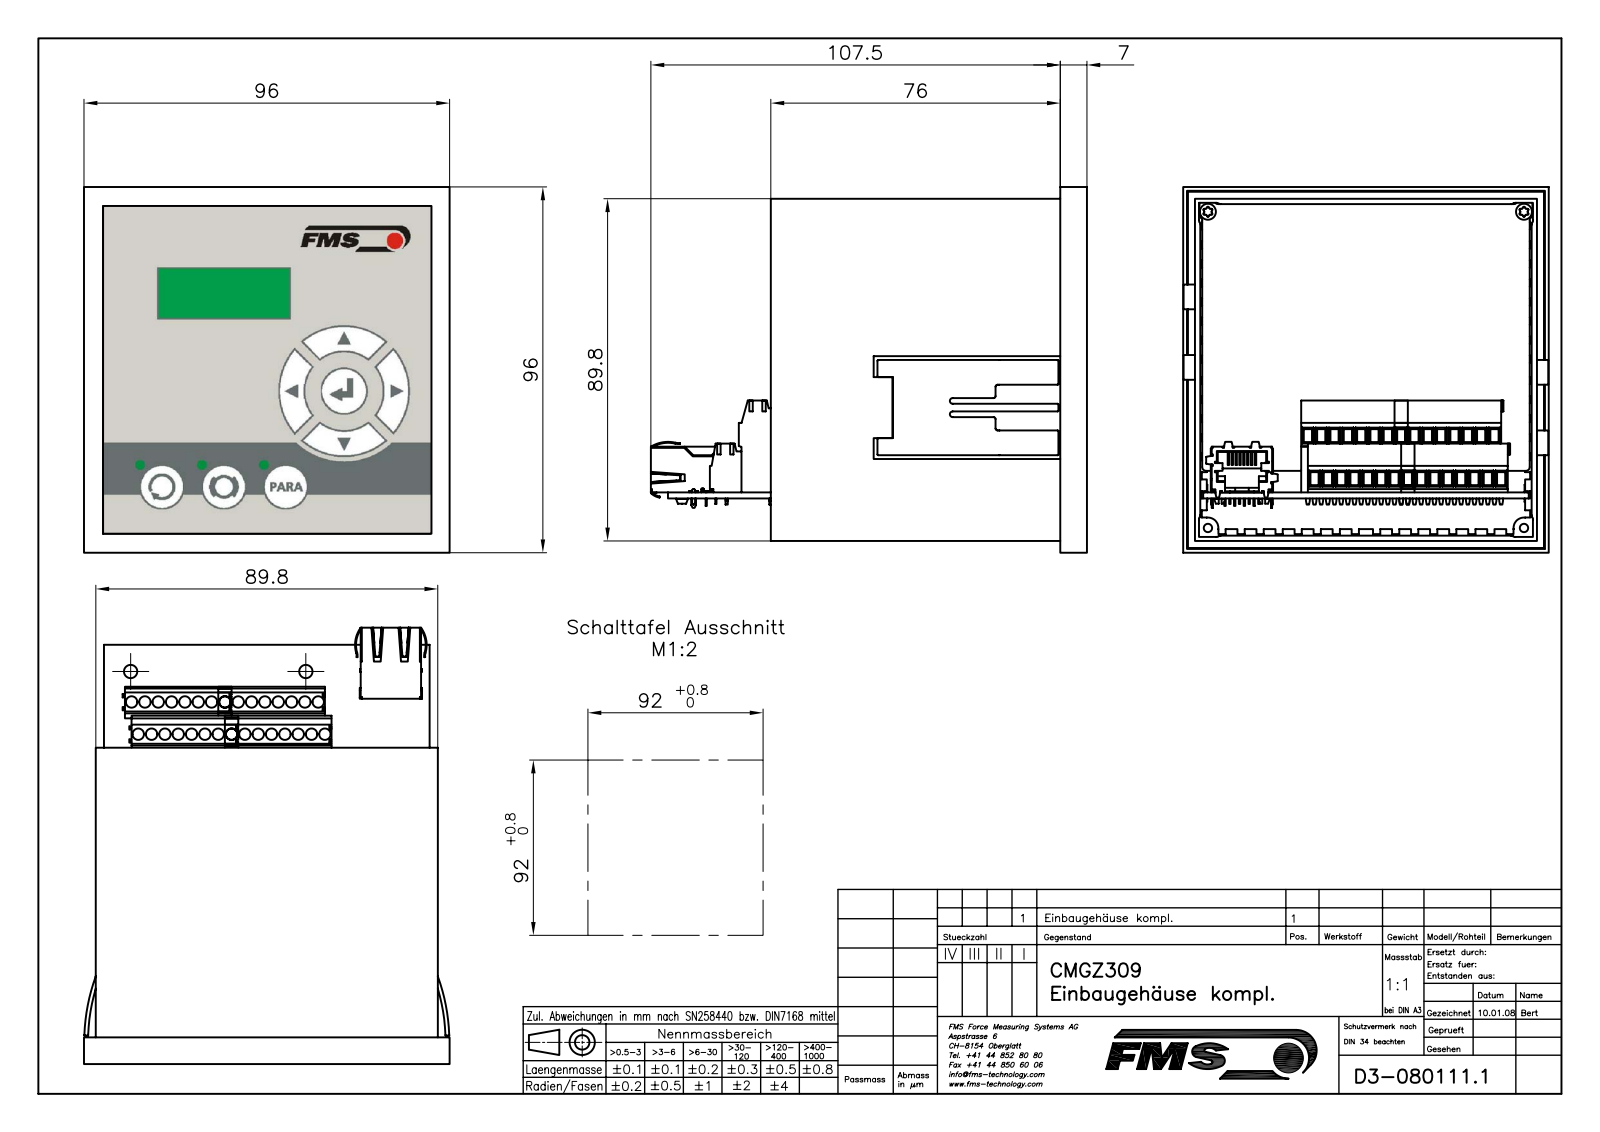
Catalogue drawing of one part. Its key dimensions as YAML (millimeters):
part_name: "E0801111; E0801094; TEIL1; TEIL2 (+7 more)"
step_written_by: "Mechanical Desktop 2009 (CONFIG_CONTROL_DESIGN)"
units: millimeters
bodies: {solids: 14, faces: 2012, planar: 1659, cylindrical: 289, other: 64}
overall_size: [114.5, 96, 96]
volume: 125984
surface_area: 141304
round_holes:
  - {diameter: 3, count: 30}
  - {diameter: 2.2, count: 8}
  - {diameter: 1, count: 4}
  - {diameter: 3.5, count: 3}
  - {diameter: 2.5, count: 2}
round_bosses_or_shafts:
  - {diameter: 4.2, count: 2}
  - {diameter: 2.67, count: 2}
partial_cylinders:
  - {radius: 0.25, count: 24}
  - {radius: 1, count: 24}
  - {radius: 0.2, count: 20}
  - {radius: 0.25, count: 19}
  - {radius: 0.5, count: 10}
  - {radius: 2.75, count: 6}
  - {radius: 0.1, count: 4}
  - {radius: 0.36, count: 4}
face_to_face_distances: [3.1, 89.8, 1, 86.7, 1.5, 1.8, 88, 1.3, 84.9, 1.6]
hole_center_spacings: [3.5, 7, 10.5, 8.63, 14, 9.95, 12.16, 17.5]
